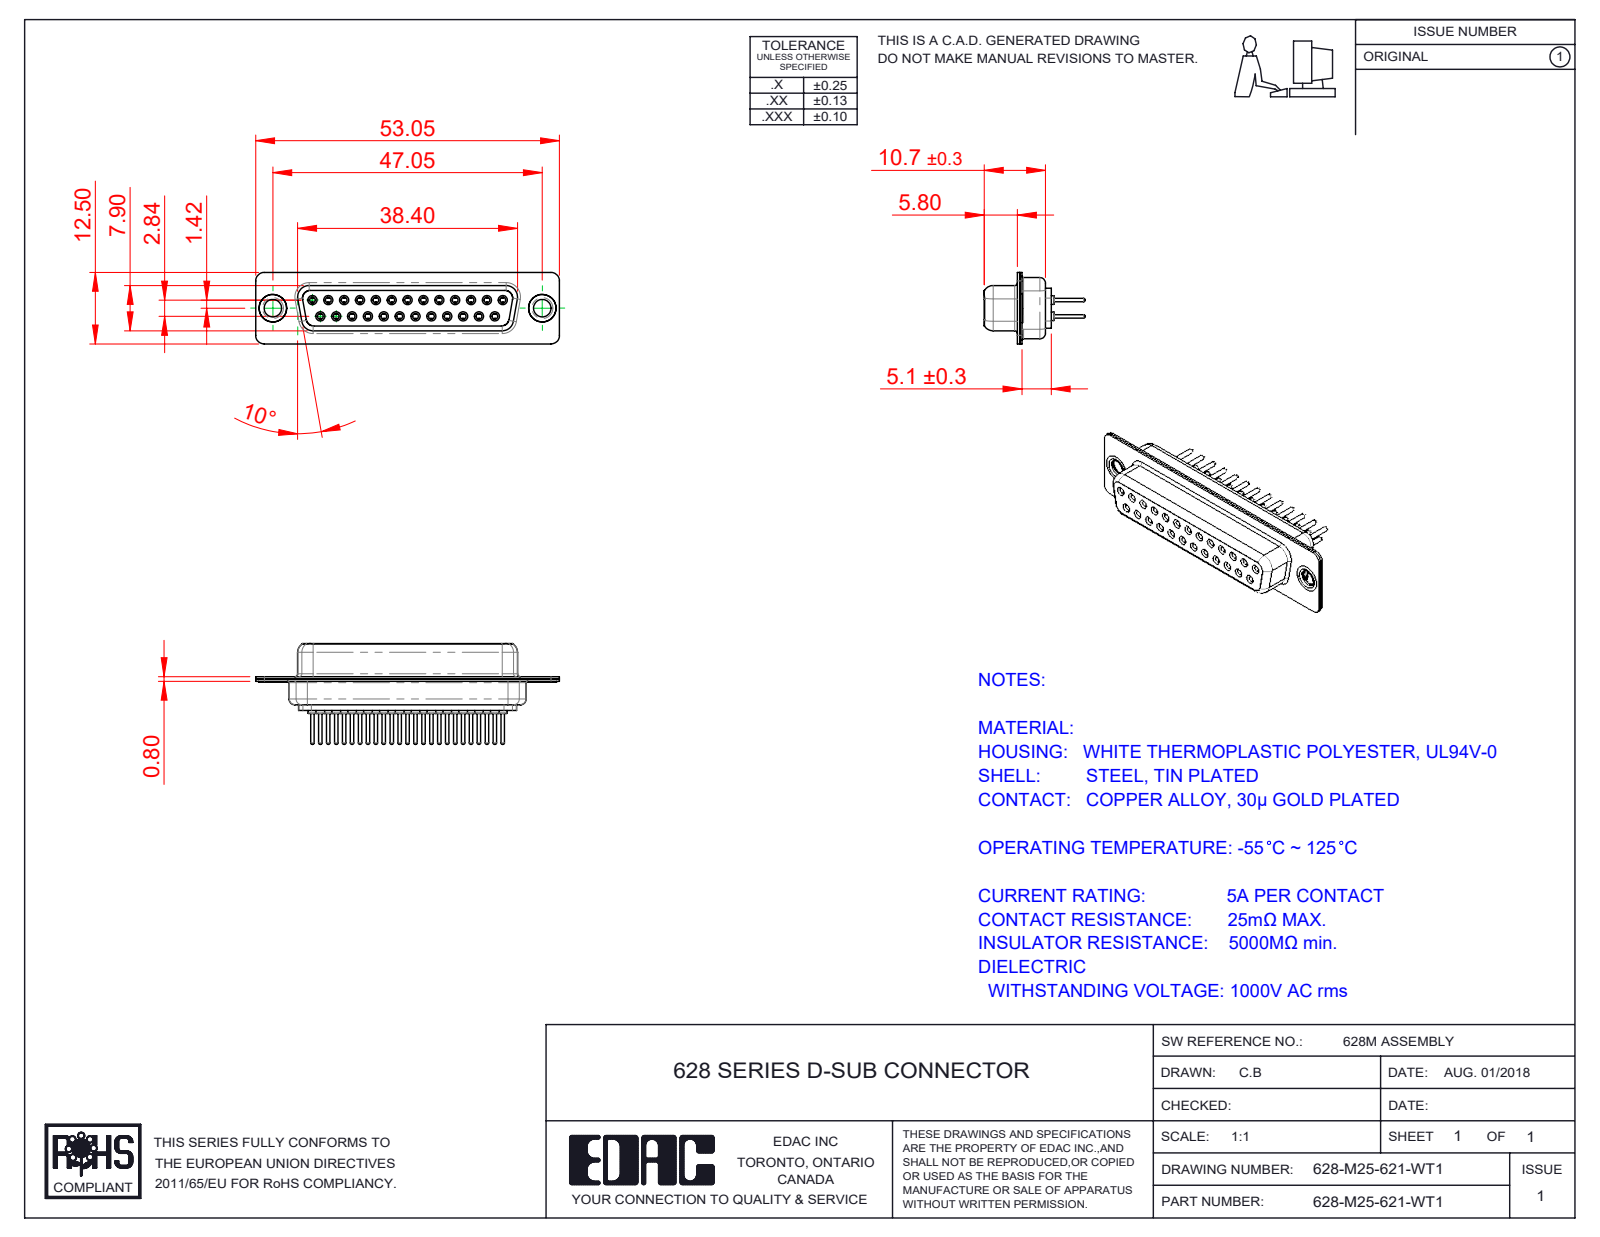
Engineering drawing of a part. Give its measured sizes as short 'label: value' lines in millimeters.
name: 628M Contact Row 1_21; 628M Shell Front_25 Contacts; 628M Contact Row 2_21; 628M Shell Rear_25 Contacts (+3 more)
written by: SolidWorks 2020 (CONFIG_CONTROL_DESIGN)
unit: mm
bodies: 30 solids, 1628 faces (442 planar, 596 cylindrical, 590 other)
size: 53.05 × 17.6 × 12.5
volume: 3 662 mm³; area: 9 001 mm²
holes: 25× ⌀1, 25× ⌀1.1, 25× ⌀1.7, 25× ⌀1.8, 25× ⌀2, 2× ⌀3.05, 2× ⌀4, 2× ⌀4.8
bosses: 25× ⌀2.2, 25× ⌀1.6, 25× ⌀1.5, 25× ⌀0.6, 2× ⌀5, 2× ⌀4.9, 2× ⌀3.55
rounds: 16× R1.5, 12× R2, 8× R1.35, 8× R1.6, 4× R0.25, 4× R0.5, 4× R0.6, 4× R0.65
face distances: 0.4, 1.4, 0.45, 8.45, 8.9, 6.2, 1.8, 7.05, 1, 1.85
hole spacings: 3.16, 2.77, 5.54, 8.31, 11.08, 13.85, 5.04, 7.49
